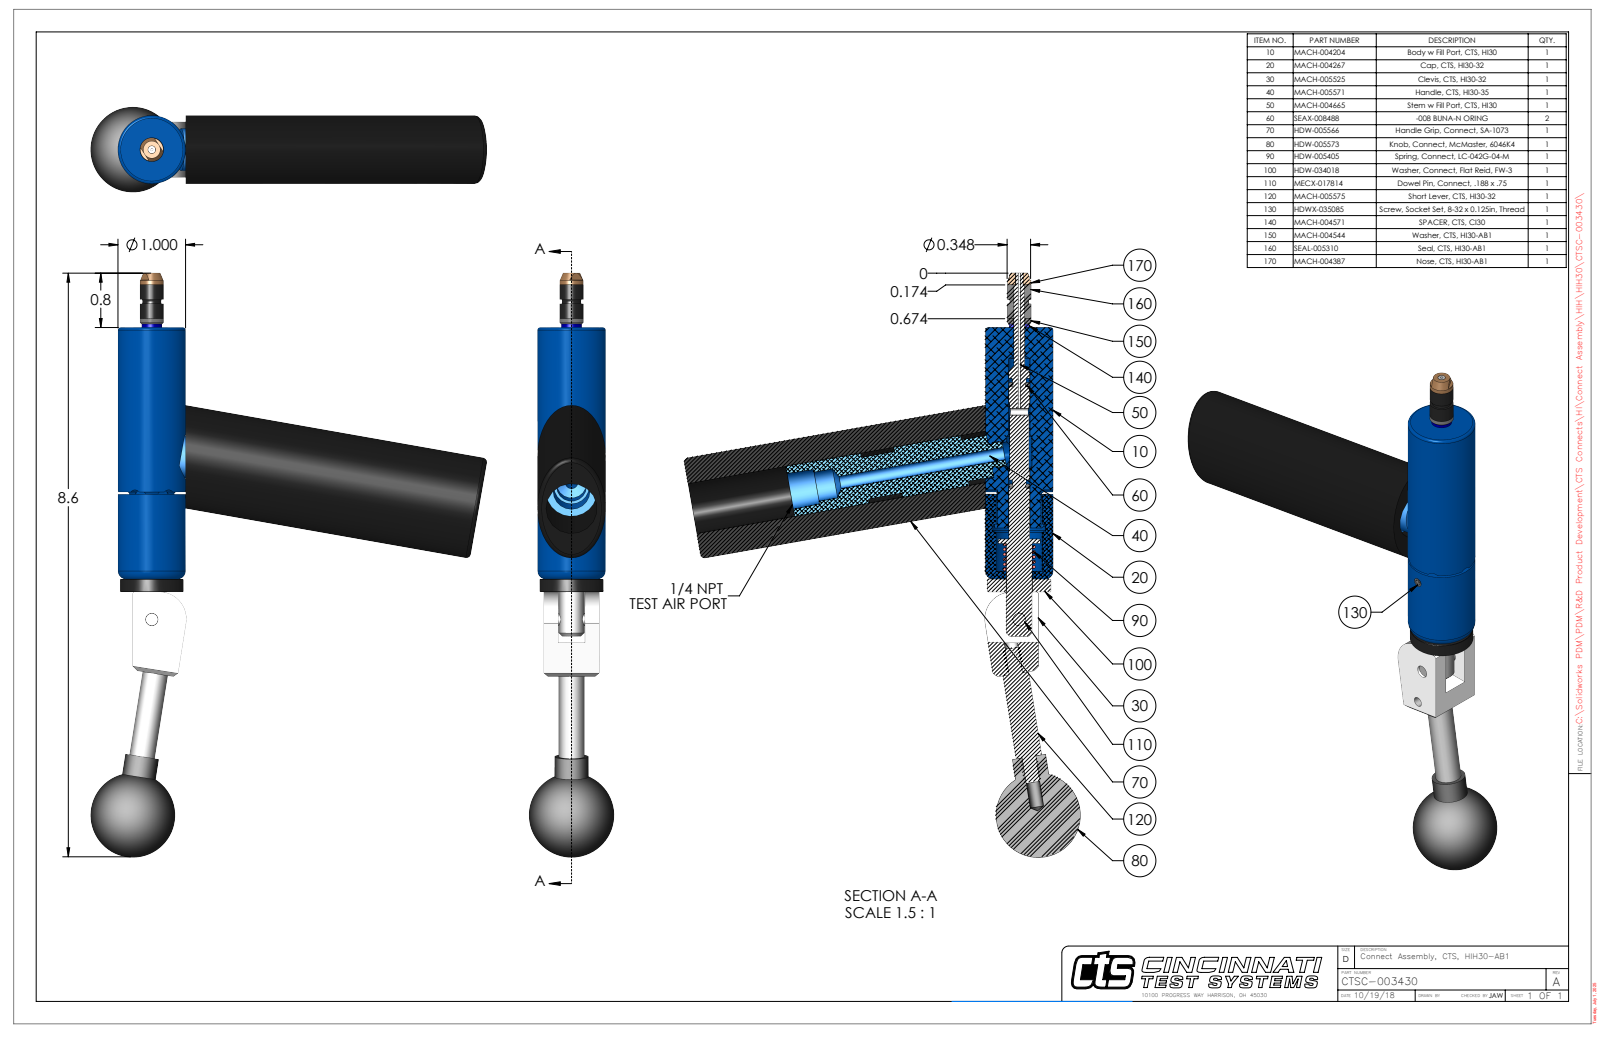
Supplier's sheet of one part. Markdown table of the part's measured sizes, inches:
| quantity | value |
| --- | --- |
| part name | CTSC-003430 |
| STEP written by | SolidWorks 2023 (AUTOMOTIVE_DESIGN) |
| units | inches |
| bodies | 11 solids, 290 faces (100 planar, 125 cylindrical, 65 other) |
| overall size | 8.63 × 5.856 × 1.25 |
| volume | 9.131 in³ |
| surface area | 73.16 in² |
| round holes (diameter × count) | 0.201 × 2, 0.04 × 1, 0.108 × 1, 0.109 × 1, 0.113 × 1, 0.136 × 1, 0.15 × 1, 0.155 × 1, 0.161 × 1, 0.164 × 1, 0.187 × 1, 0.189 × 1 |
| round bosses / shafts (diameter × count) | 1 × 1, 0.936 × 1, 0.75 × 1, 0.62 × 1, 0.5 × 1, 0.38 × 1, 0.375 × 1, 0.35 × 1 |
| partial cylindrical surfaces (radius × count) | 0.093 × 6, 0.015 × 1, 0.325 × 1, 0.4 × 1, 0.478 × 1 |
| main face-to-face distances | 0.21, 0.602, 0.812, 0.187, 3.717, 3.904, 0.785, 0.391, 2.463, 1.253 |
| hole center spacings | 0.599, 1.658, 2.252 |
